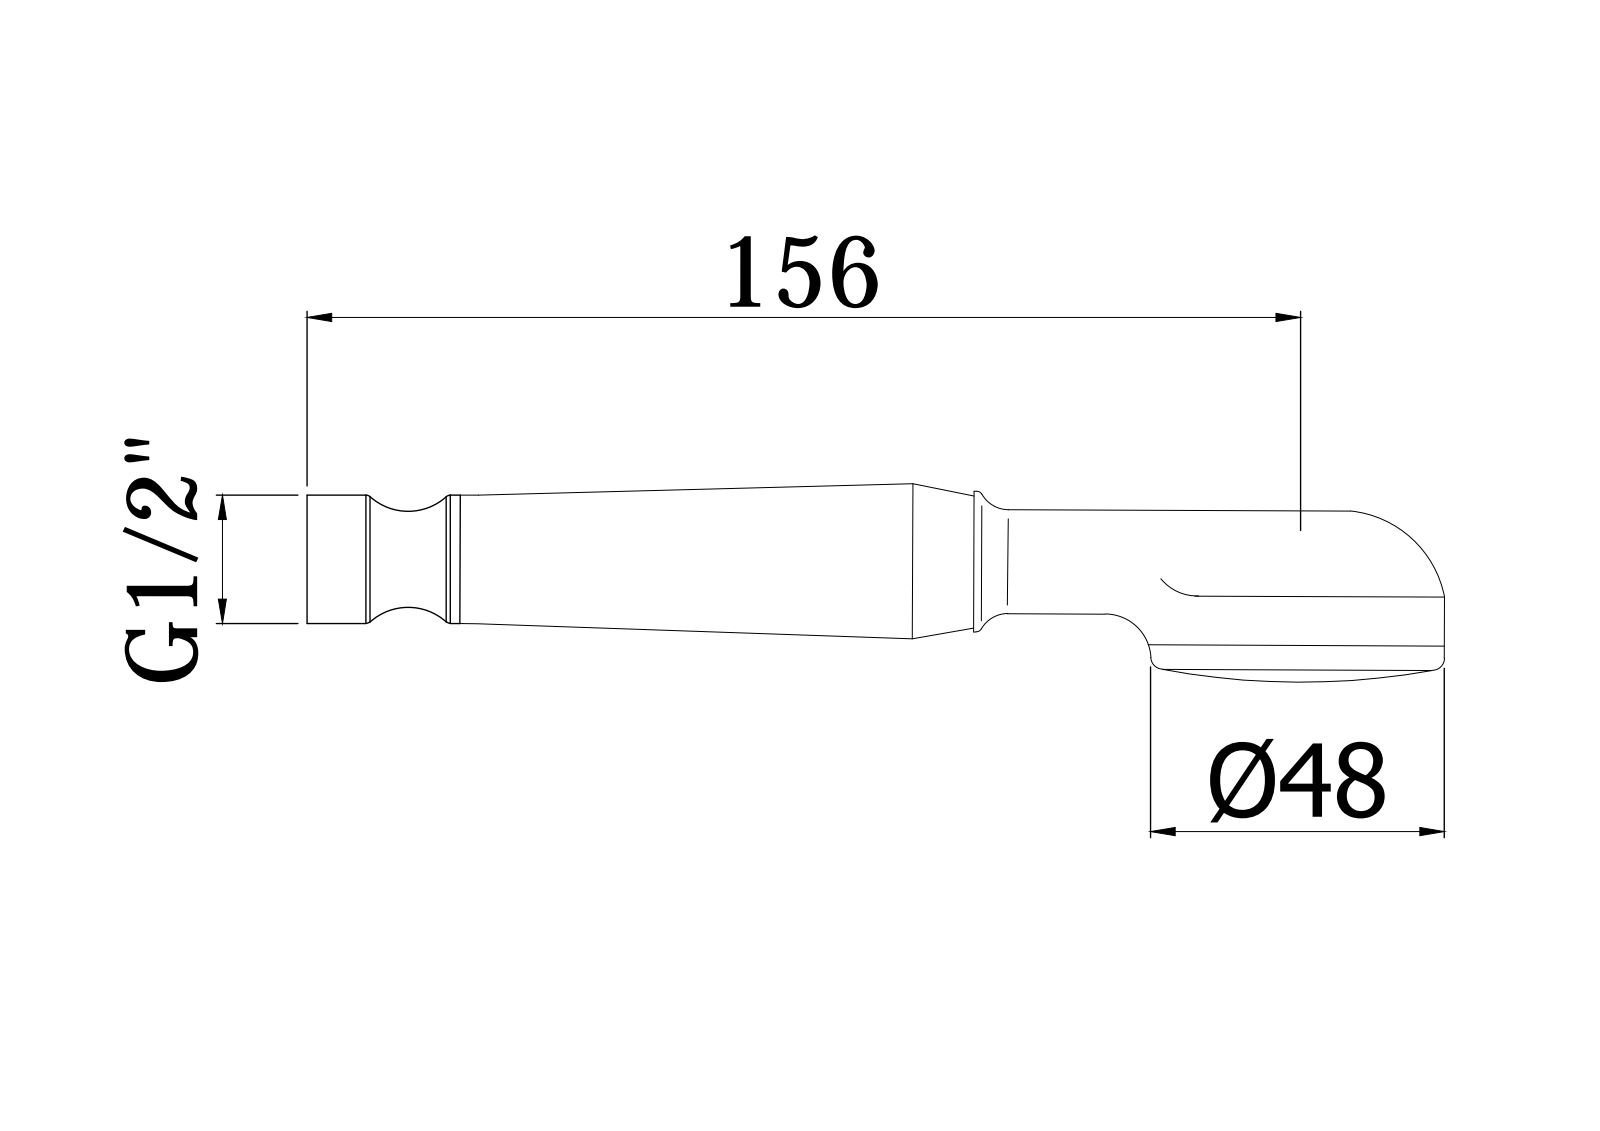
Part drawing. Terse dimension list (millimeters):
name: ZDOC009CR
written by: CREO PARAMETRIC BY PTC INC, 2020044 (CONFIG_CONTROL_DESIGN)
unit: mm
bodies: 0 solids, 236 faces (18 planar, 200 cylindrical, 18 other)
size: 182.41 × 54.83 × 40
holes: 96× ⌀1
bosses: 1× ⌀53.5, 1× ⌀20.5, 1× ⌀17
face distances: 8, 3, 105, 16, 19, 11, 97, 89, 86, 5
hole spacings: 7.64, 15.05, 3.83, 25.24, 31.11, 33.7, 39.88, 42.5
